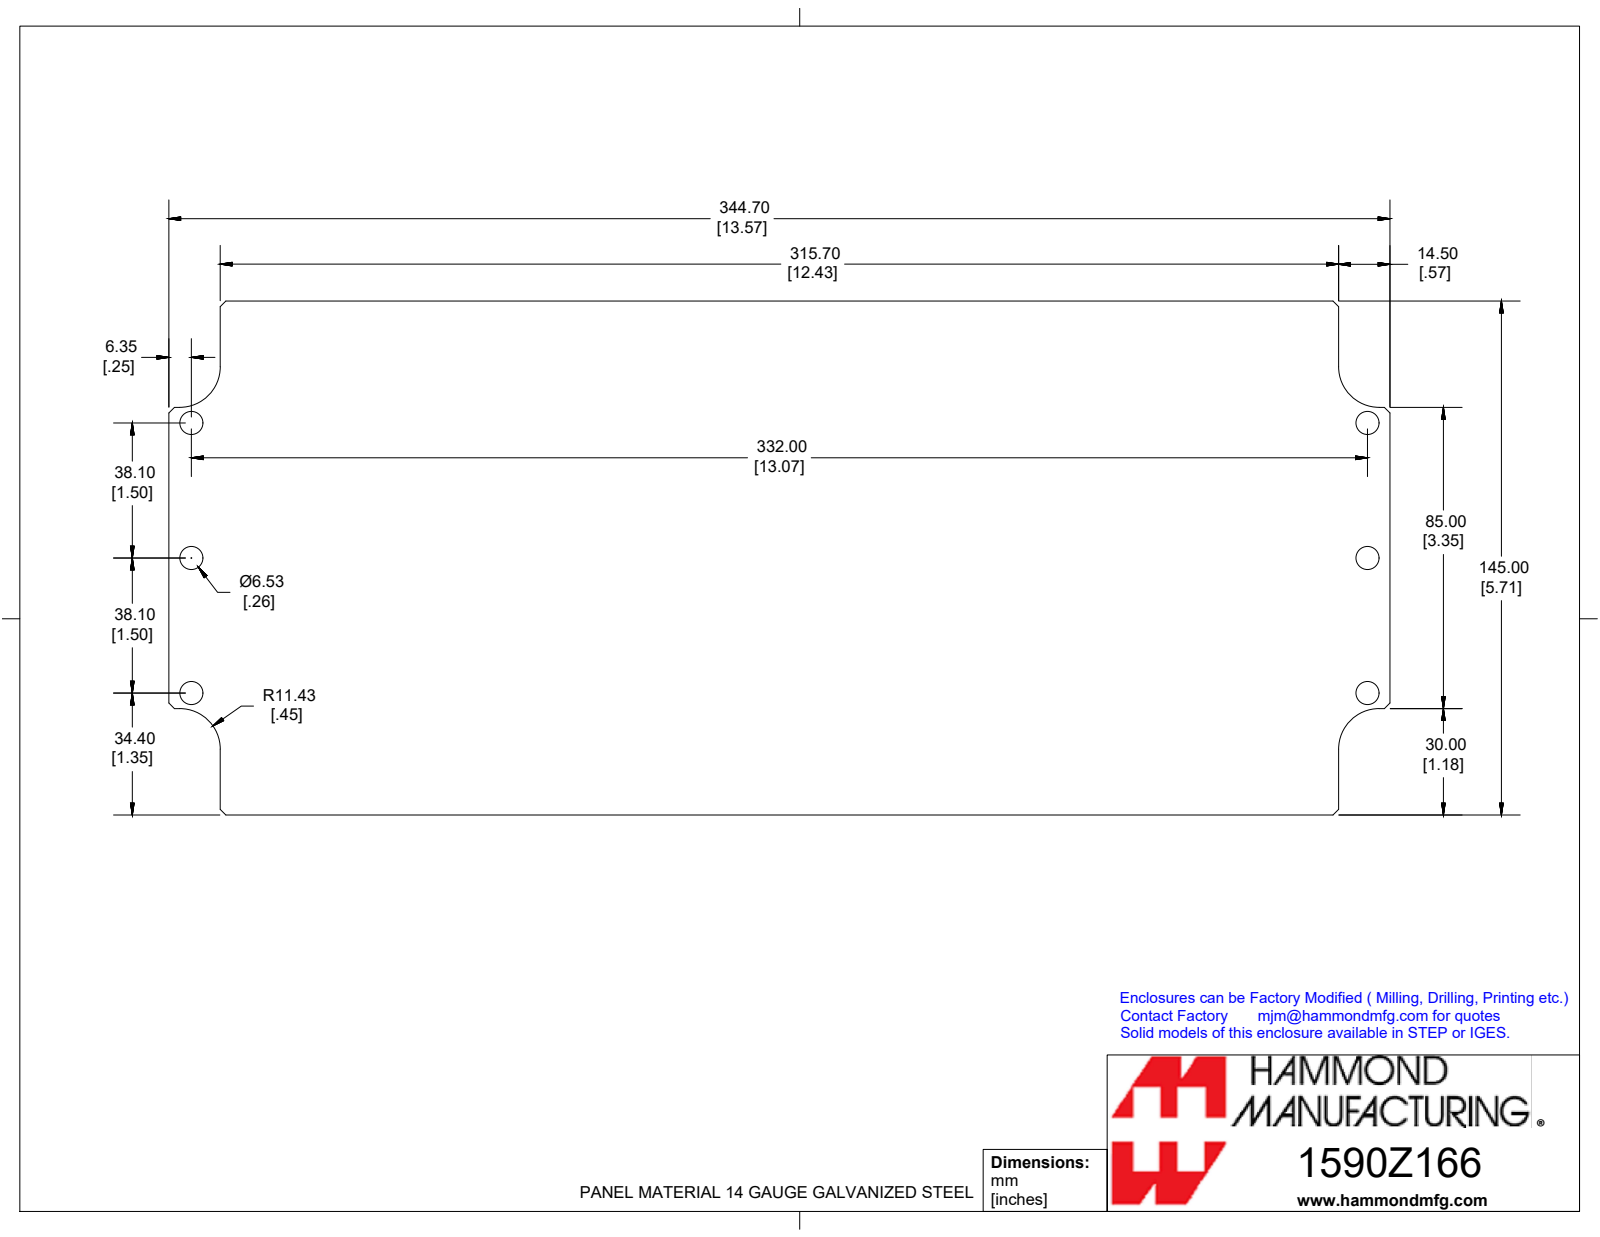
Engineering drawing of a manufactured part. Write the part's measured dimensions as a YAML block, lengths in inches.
part_name: "1590Z166PL"
step_written_by: "SolidWorks 2019 (CONFIG_CONTROL_DESIGN)"
units: inches
bodies: {solids: 1, faces: 32, planar: 22, cylindrical: 10, other: 0}
overall_size: [13.571, 5.709, 0.064]
volume: 4.739
surface_area: 151.9
round_holes:
  - {diameter: 0.257, count: 6}
partial_cylinders:
  - {radius: 0.45, count: 4}
face_to_face_distances: [0.063, 5.709, 13.571, 0.571, 13, 12.429, 0.431, 12.304, 1.181, 4.528]
hole_center_spacings: [1.5, 13.157, 13.071, 3, 13.411]
